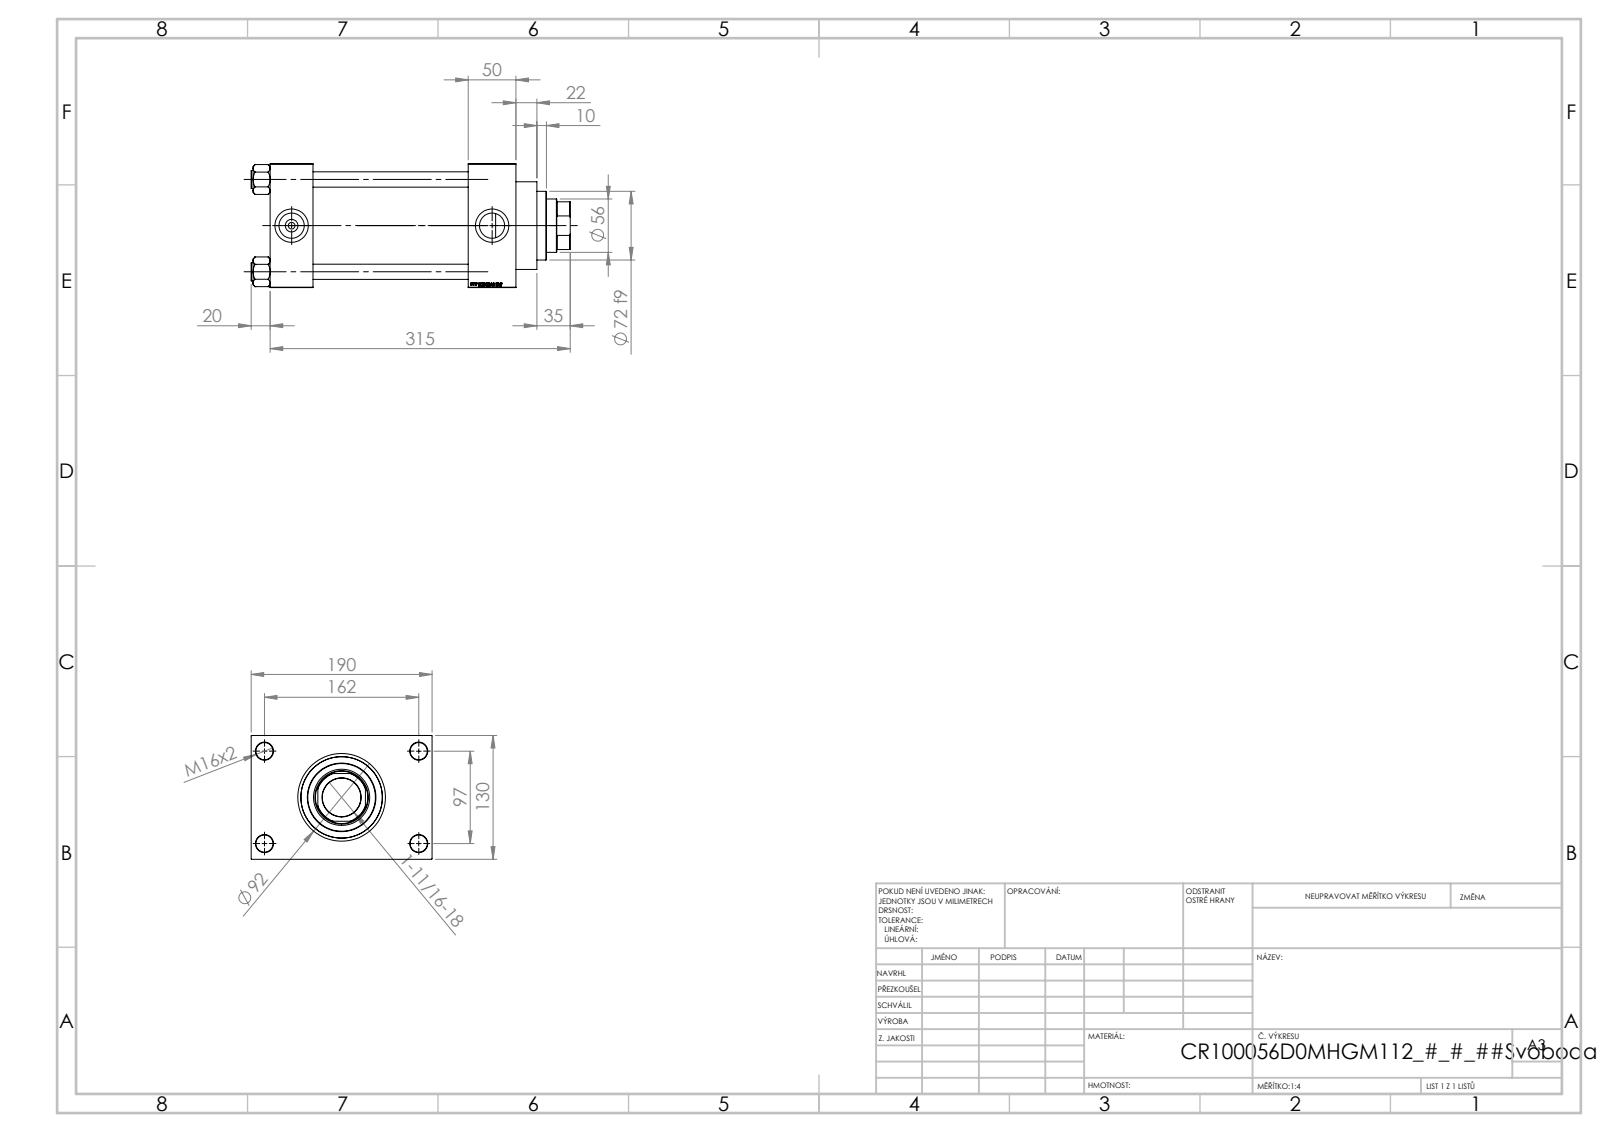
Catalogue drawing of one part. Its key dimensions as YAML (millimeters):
part_name: "V215_VC_A; V215CR_VCP_D; V215CR_D_Body; NUT_M5_D (+1 more)"
step_written_by: "SolidWorks 2019 (CONFIG_CONTROL_DESIGN)"
units: millimeters
bodies: {solids: 11, faces: 1151, planar: 545, cylindrical: 88, other: 518}
overall_size: [335, 190, 130]
volume: 3018000
surface_area: 456586
round_holes:
  - {diameter: 16, count: 4}
  - {diameter: 18, count: 4}
  - {diameter: 7, count: 2}
  - {diameter: 26.44, count: 2}
  - {diameter: 35, count: 2}
  - {diameter: 40.5, count: 1}
  - {diameter: 56, count: 1}
  - {diameter: 59, count: 1}
  - {diameter: 76, count: 1}
  - {diameter: 85.5, count: 1}
  - {diameter: 100, count: 1}
round_bosses_or_shafts:
  - {diameter: 19, count: 4}
  - {diameter: 106, count: 1}
  - {diameter: 92, count: 1}
  - {diameter: 72, count: 1}
partial_cylinders:
  - {radius: 27, count: 1}
face_to_face_distances: [130, 50, 45, 208, 163, 258, 213, 30, 160, 190]
hole_center_spacings: [32.55, 68.52, 94.41, 96.9, 102.27, 129.45, 161.73, 97]
